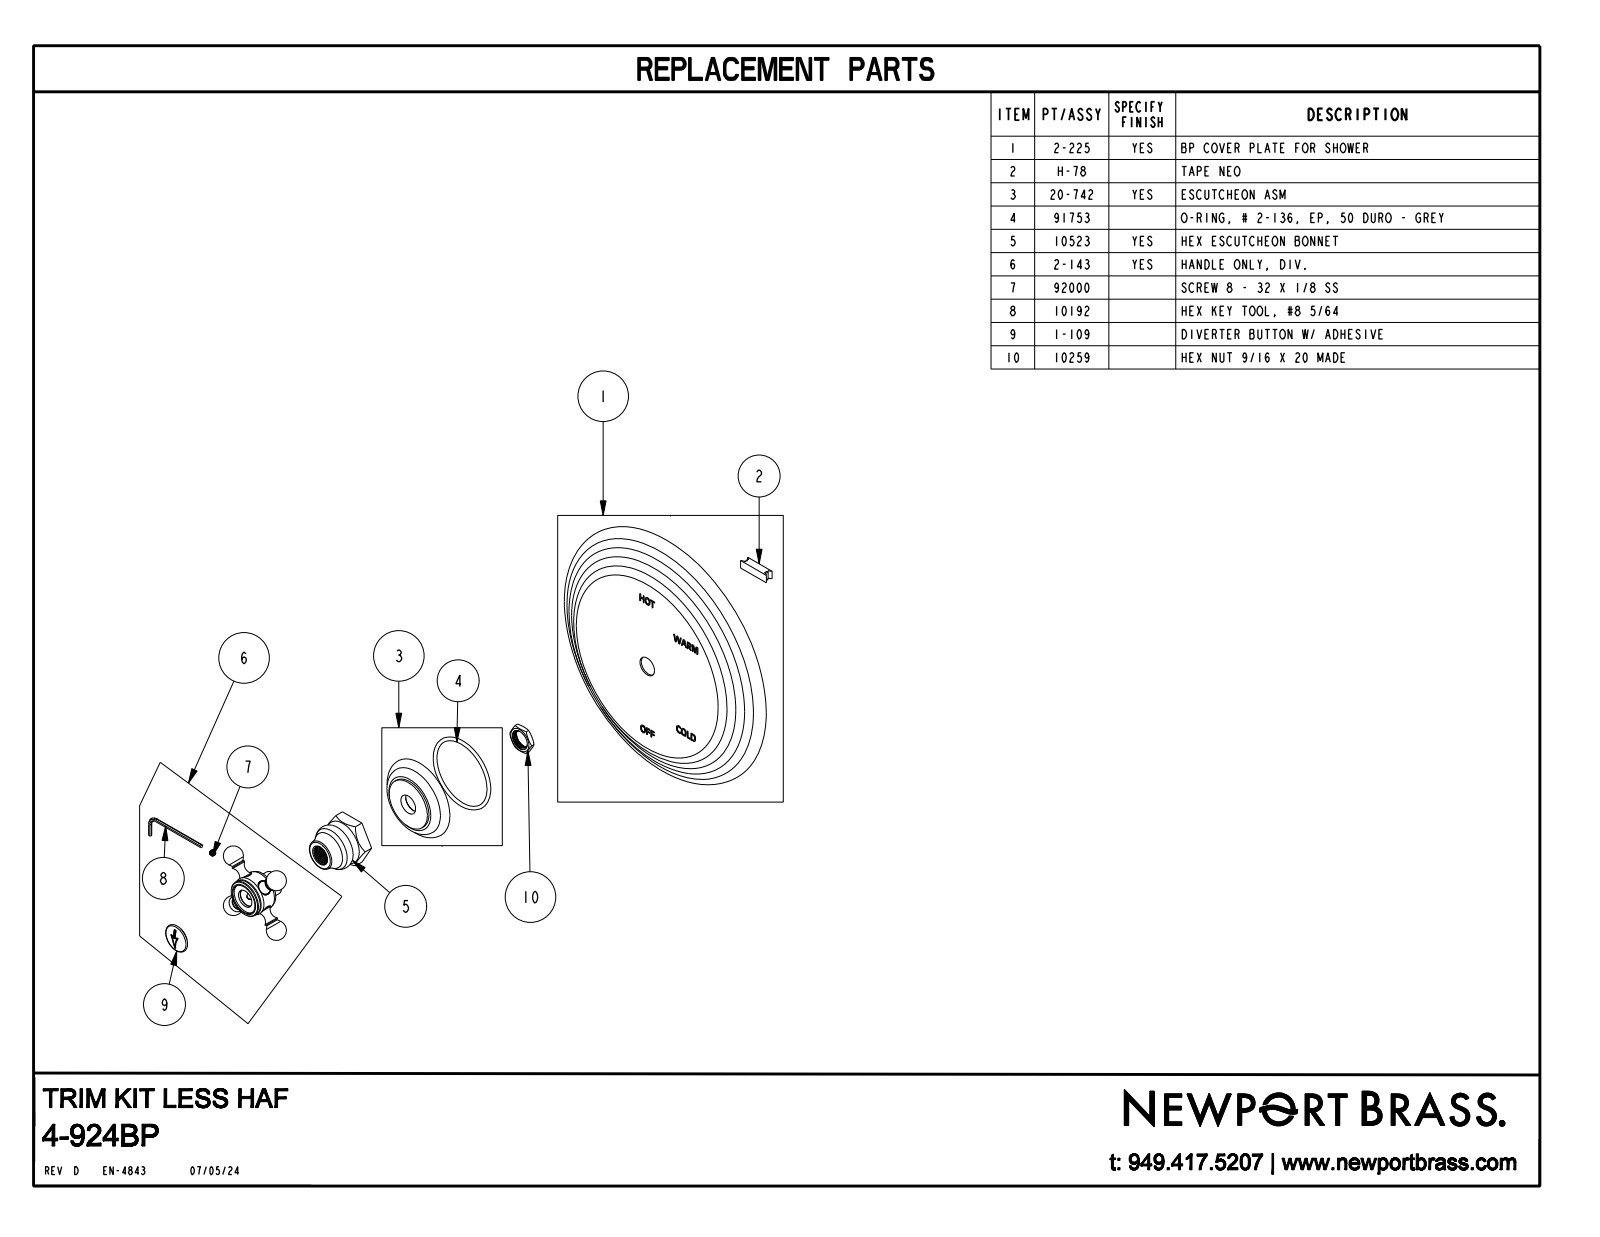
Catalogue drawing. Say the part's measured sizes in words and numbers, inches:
The part is named "4-924BP". Its 3-D file was written by "CREO PARAMETRIC BY PTC INC, 2018400 (CONFIG_CONTROL_DESIGN)". It is 1 solid with 378 faces: 165 planar, 33 cylindrical and 180 other. Overall it measures 7.75 by 7.75 by 3.656 inches. Its volume is 31.8 cubic inches and its surface area 117.6 square inches. Round holes: 2 of diameter 0.41, 1 of diameter 0.855. Round bosses or shafts: 2 of diameter 0.392, 1 of diameter 1.482, 1 of diameter 1.055, 1 of diameter 0.687, 1 of diameter 0.4. Partial cylindrical surfaces (rounded edges, fillets, slot ends): 2 of radius 0.015, 2 of radius 1, 2 of radius 1.02, 1 of radius 0.02. The main face-to-face distances are 0.754, 1.313, 2.441, 1.687, 1.129, 0.375, 1.312, 0.75, 0.379, 1.691.
